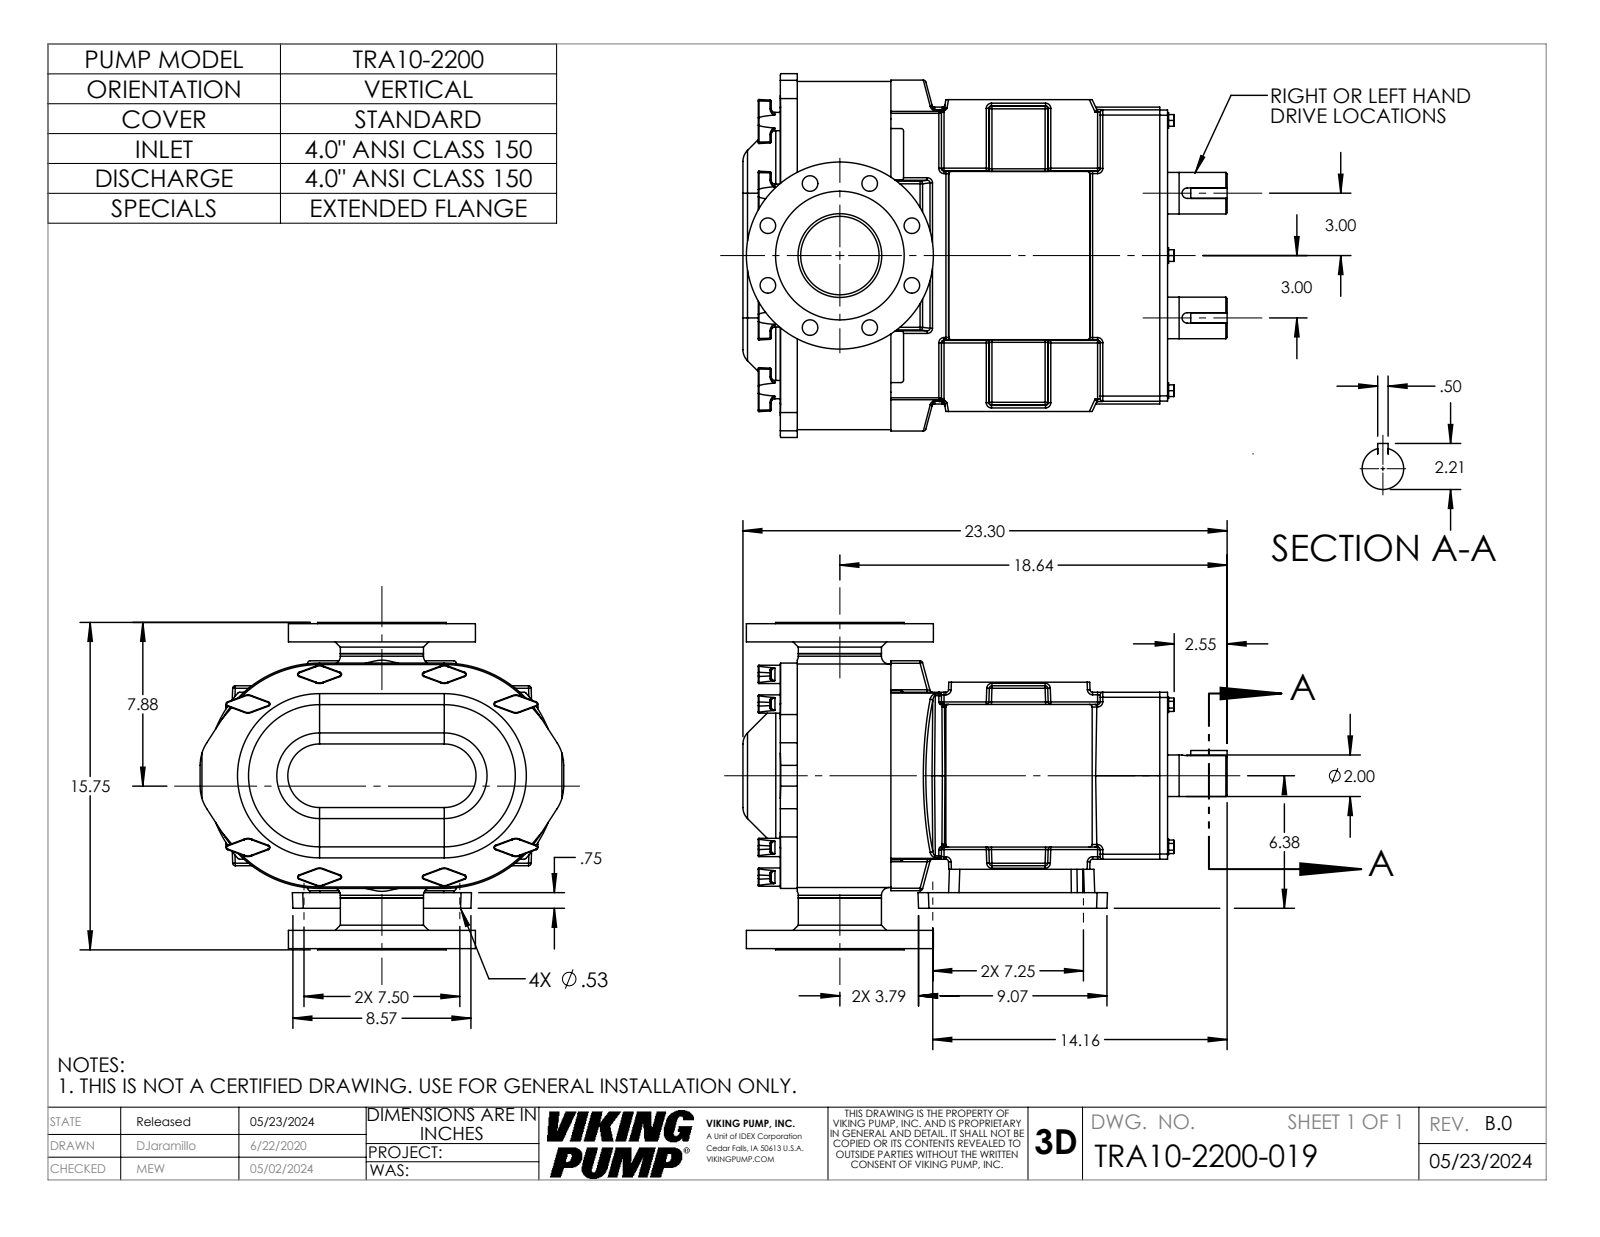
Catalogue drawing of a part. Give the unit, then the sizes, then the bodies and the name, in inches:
Units: inches
Overall size (bounding box): 23.301 × 17.5 × 15.75
Round holes (diameter × count): ⌀0.75 ×8, ⌀0.531 ×4, ⌀3.775 ×1, ⌀3.775 ×1, ⌀4.03 ×1
Round bosses / shafts (diameter × count): ⌀0.88 ×8, ⌀0.75 ×6, ⌀1.999 ×2, ⌀9 ×1, ⌀6.19 ×1, ⌀4 ×1
Partial cylindrical surfaces — rounded edges, fillets, slot ends (radius × count): R0.125 ×138, R0.03 ×32, R0.06 ×32, R0.25 ×16, R0.5 ×16, R0.75 ×4, R2 ×4, R0.251 ×2
Main face-to-face distances: 4.505, 17.82, 13.315, 5.365, 0.86, 12.455, 0.484, 8.516, 0.878, 14.752
Hole centre spacings: 2.87, 3.75, 5.303, 6.929, 7.5, 2.524, 3.05, 5.282
Volume: 2 707 in³ · Surface area: 2 469 in²
Bodies: 5 solids, 954 faces (262 planar, 380 cylindrical, 312 other)
Part name (STEP PRODUCT): TRA10-2200-GEARBOX-V; TRA10-2200-019; 2200FLG150-40; TRA10-2200-COVER-STD (+2 more)
STEP written by: SolidWorks 2023 (AUTOMOTIVE_DESIGN)
